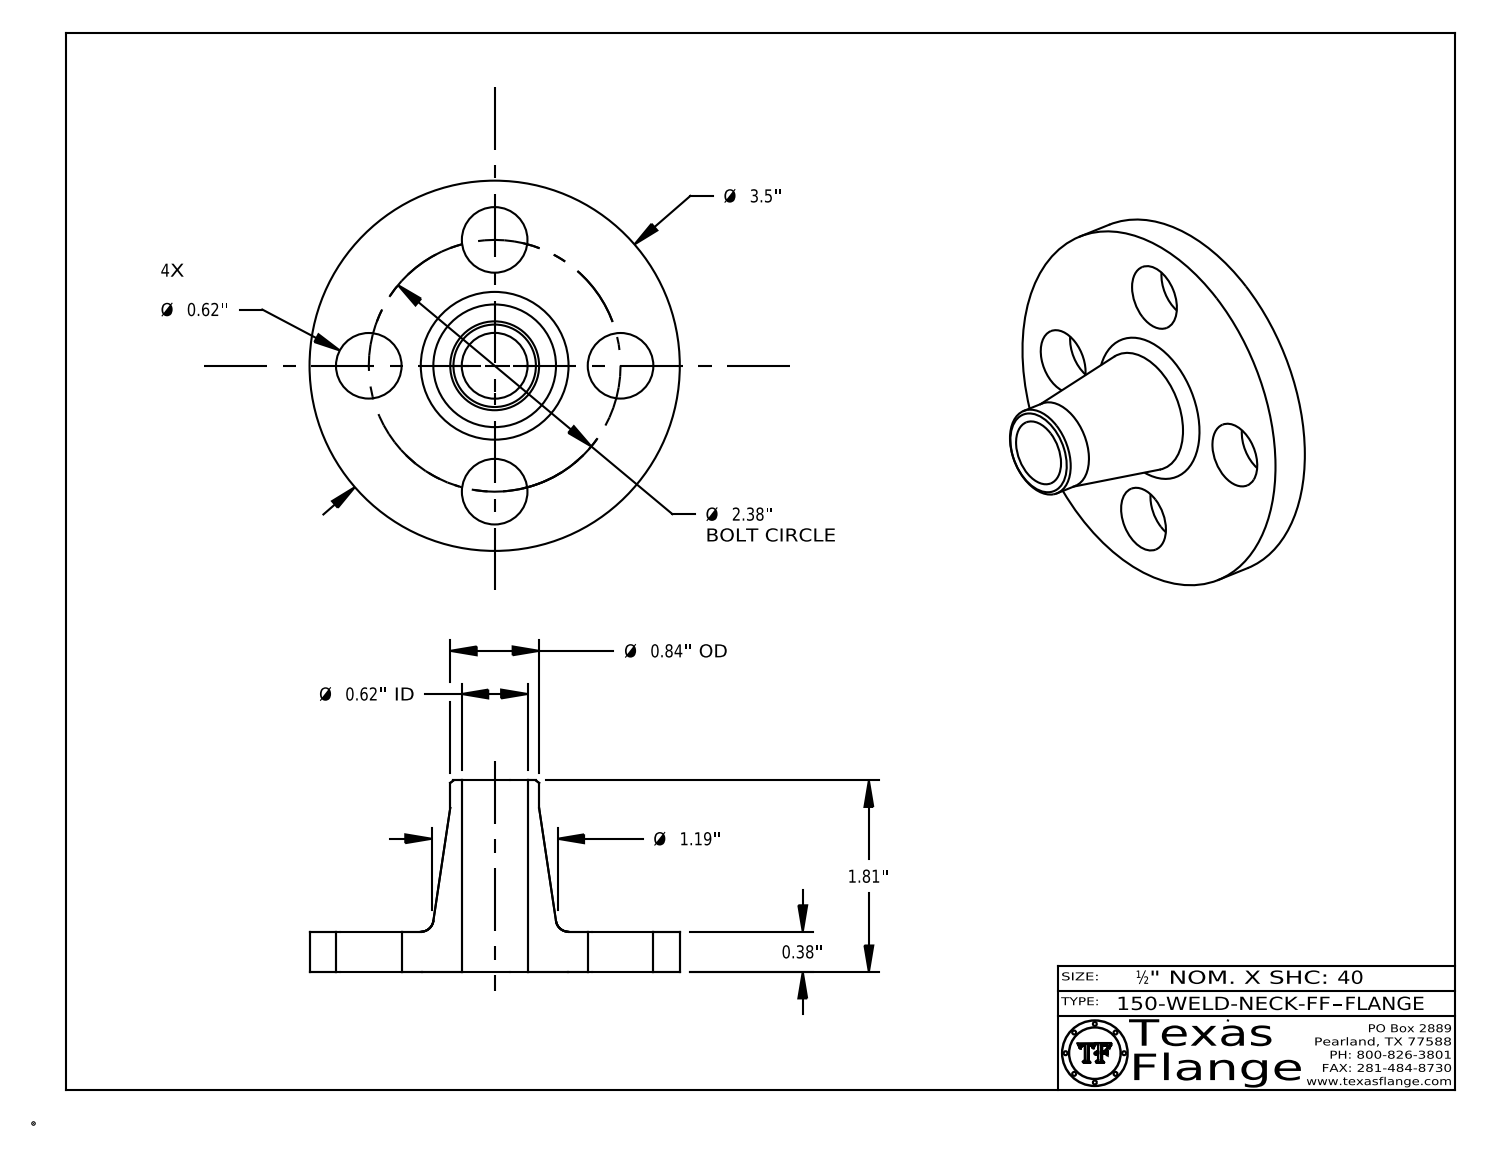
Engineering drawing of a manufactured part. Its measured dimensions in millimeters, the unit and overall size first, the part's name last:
Units: millimetres
Overall size (bounding box): 88.9 × 88.9 × 46
Round holes (diameter × count): ⌀15.7 ×4, ⌀12.6 ×1, ⌀15.8 ×1
Round bosses / shafts (diameter × count): ⌀0.8 ×8, ⌀88.9 ×1, ⌀21.3 ×1, ⌀9.9 ×1
Main face-to-face distances: 9.7, 46, 36.3, 9.3, 0.4, 36.7, 3.8, 3.7, 0.7, 2.4
Hole centre spacings: 30.2, 42.7, 23.1, 55.9, 60.5, 30.2
Volume: 61 520 mm³ · Surface area: 19 820 mm²
Bodies: 1 solid, 409 faces (369 planar, 34 cylindrical, 6 other)
Part name (STEP PRODUCT): 150-WELD-NECK-FF
STEP written by: CATIA V5 STEP AP214 (AUTOMOTIVE_DESIGN)
